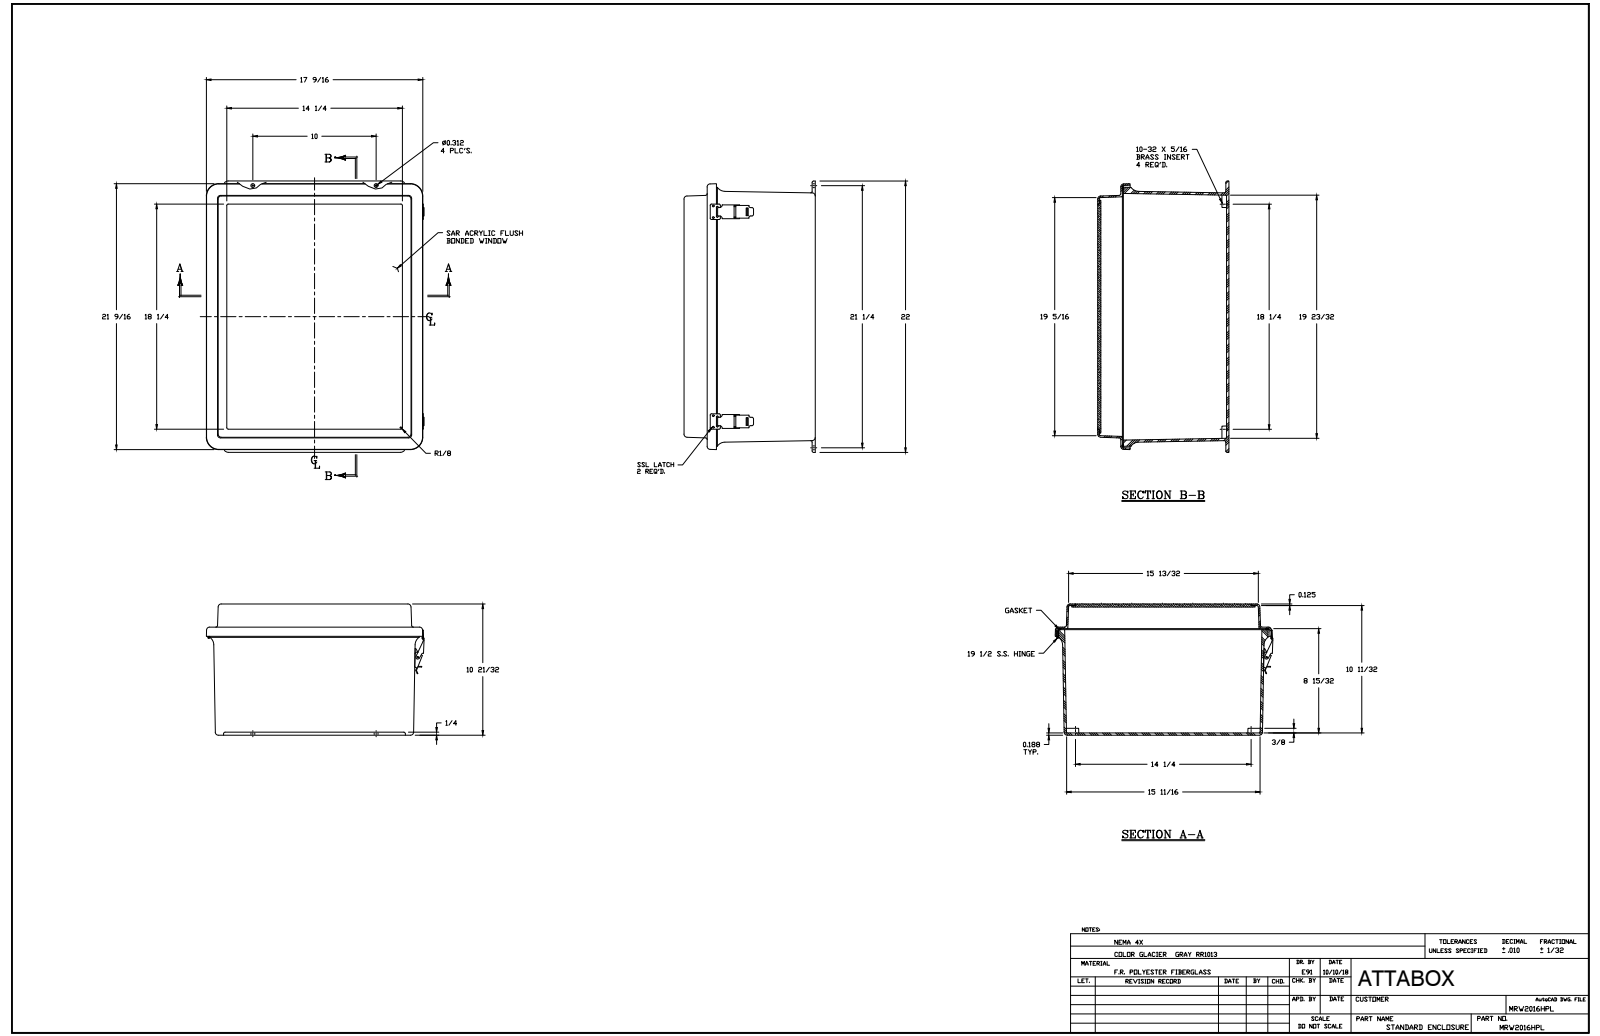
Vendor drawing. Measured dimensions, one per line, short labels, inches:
name: MRW2016HPL
written by: SolidWorks 2018 (AUTOMOTIVE_DESIGN)
unit: in
bodies: 43 solids, 1242 faces (558 planar, 517 cylindrical, 167 other)
size: 22 × 17.698 × 10.642
volume: 306.4 in³; area: 3 257 in²
holes: 24× ⌀0.14, 12× ⌀0.131, 8× ⌀0.104, 5× ⌀0.152, 4× ⌀0.13, 4× ⌀0.156, 4× ⌀0.218, 2× ⌀0.135, 2× ⌀0.375, 1× ⌀0.085, 1× ⌀0.135
bosses: 14× ⌀0.125, 12× ⌀0.25, 6× ⌀0.125, 4× ⌀0.27, 1× ⌀0.3, 1× ⌀0.17, 1× ⌀0.155, 1× ⌀0.155
rounds: 34× R0.125, 20× R0.015, 20× R0.031, 16× R0.045, 16× R0.25, 12× R0.03, 8× R0.023, 6× R0.06
face distances: 0.187, 0.188, 0.25, 10.392, 10.642, 10.454, 10.204, 0.125, 0.125, 1.75
hole spacings: 3.75, 17, 7.5, 0.937, 0.25, 3.5, 4, 7.25
